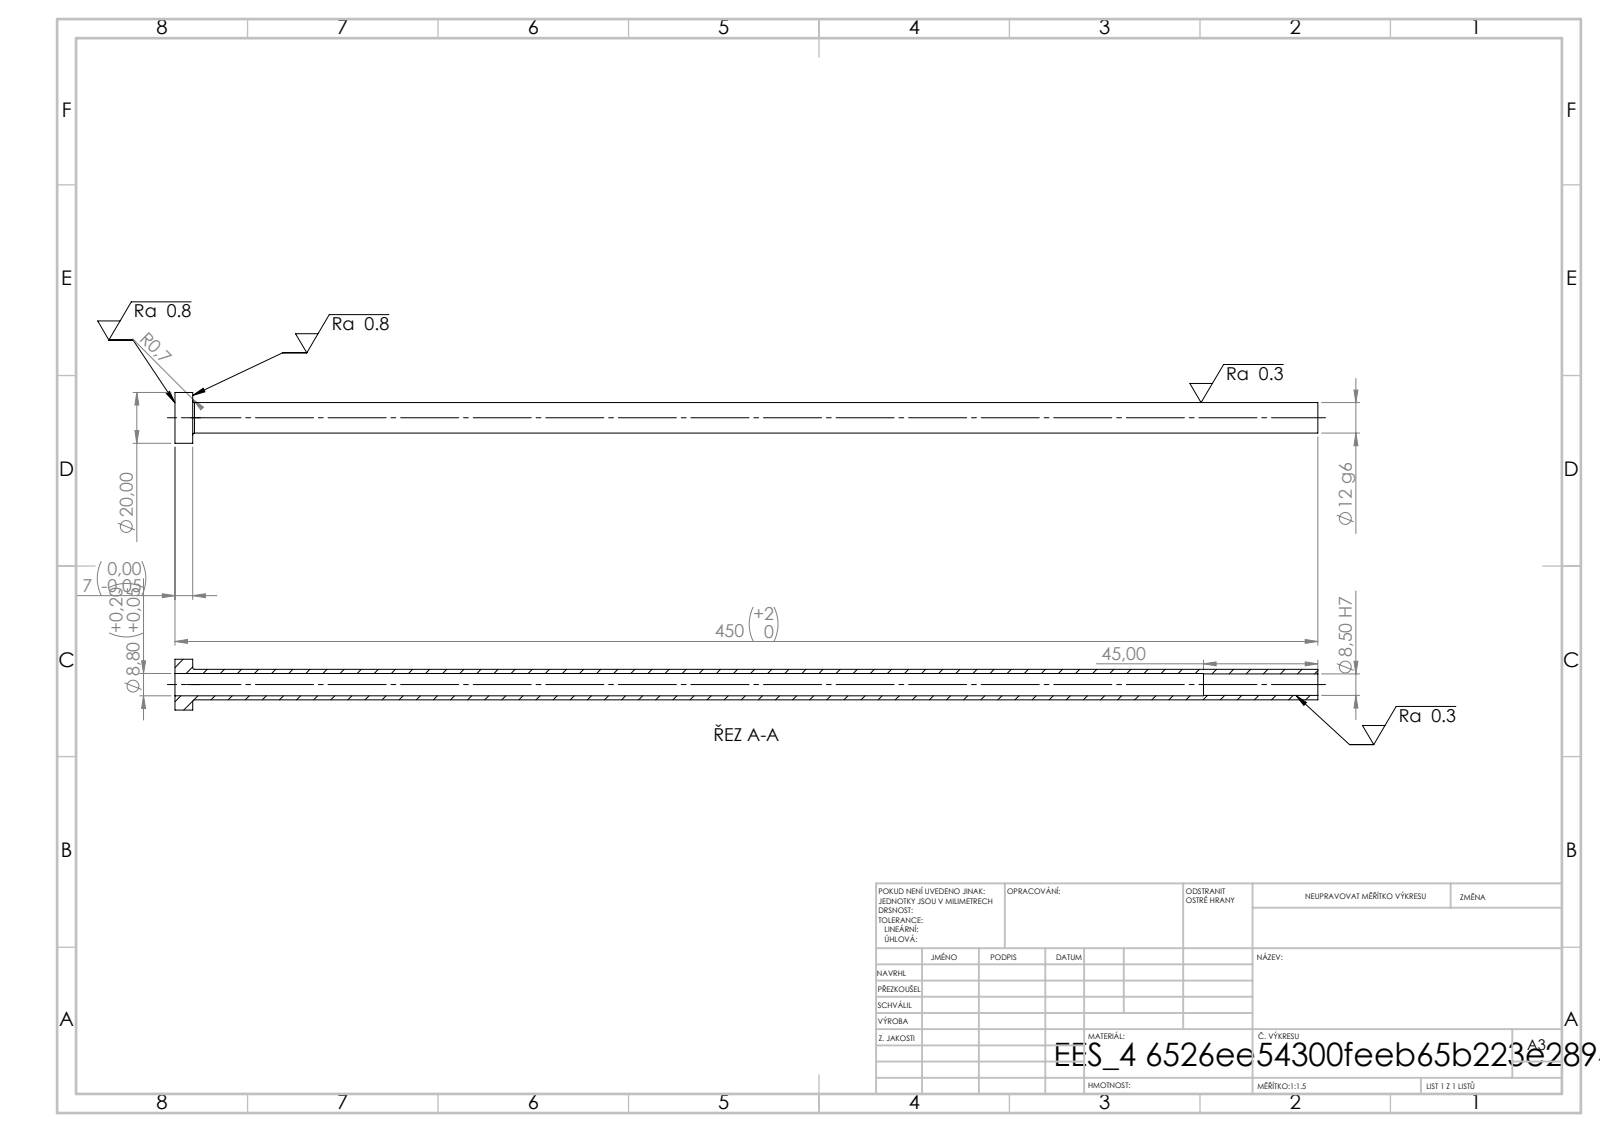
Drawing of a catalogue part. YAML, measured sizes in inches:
step_written_by: "SolidWorks 2019 (CONFIG_CONTROL_DESIGN)"
units: inches
bodies: {solids: 1, faces: 14, planar: 4, cylindrical: 8, other: 2}
overall_size: [17.717, 0.787, 0.787]
volume: 1.533
surface_area: 46.57
round_holes:
  - {diameter: 0.335, count: 1}
  - {diameter: 0.346, count: 1}
round_bosses_or_shafts:
  - {diameter: 0.787, count: 1}
  - {diameter: 0.472, count: 1}
face_to_face_distances: [0.276, 17.717, 17.441, 15.945, 15.669, 1.772]
